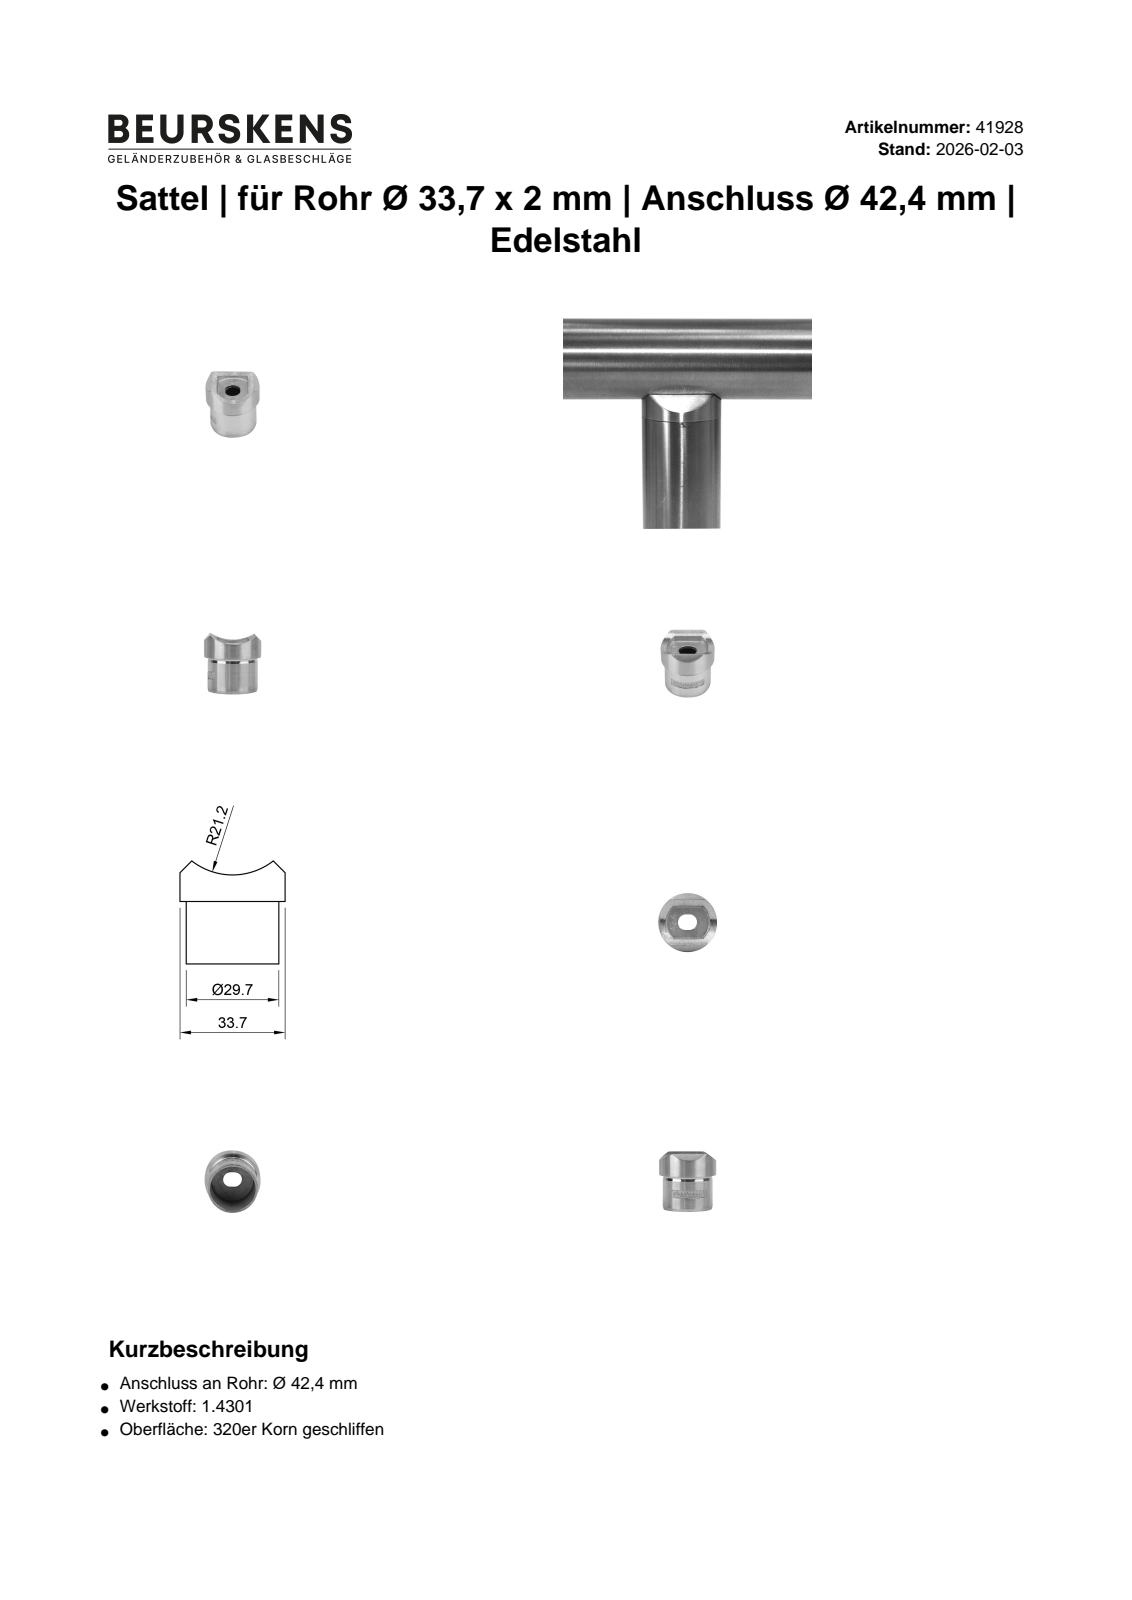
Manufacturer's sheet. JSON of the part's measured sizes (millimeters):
{"part_name": "41928", "step_written_by": "Autodesk Inventor 2022 (AUTOMOTIVE_DESIGN)", "units": "millimeters", "bodies": {"solids": 1, "faces": 20, "planar": 10, "cylindrical": 10, "other": 0}, "overall_size": [33.7, 33.7, 33], "volume_mm3": 9703, "surface_area_mm2": 6809, "round_holes": [[27.7, 1]], "round_bosses_or_shafts": [[33.7, 1], [29.7, 1]], "partial_cylinders_radius": [[4.25, 2], [21.2, 1]], "face_to_face_distances": [8.5, 20, 28.5, 20.12, 5.81, 14.31]}
